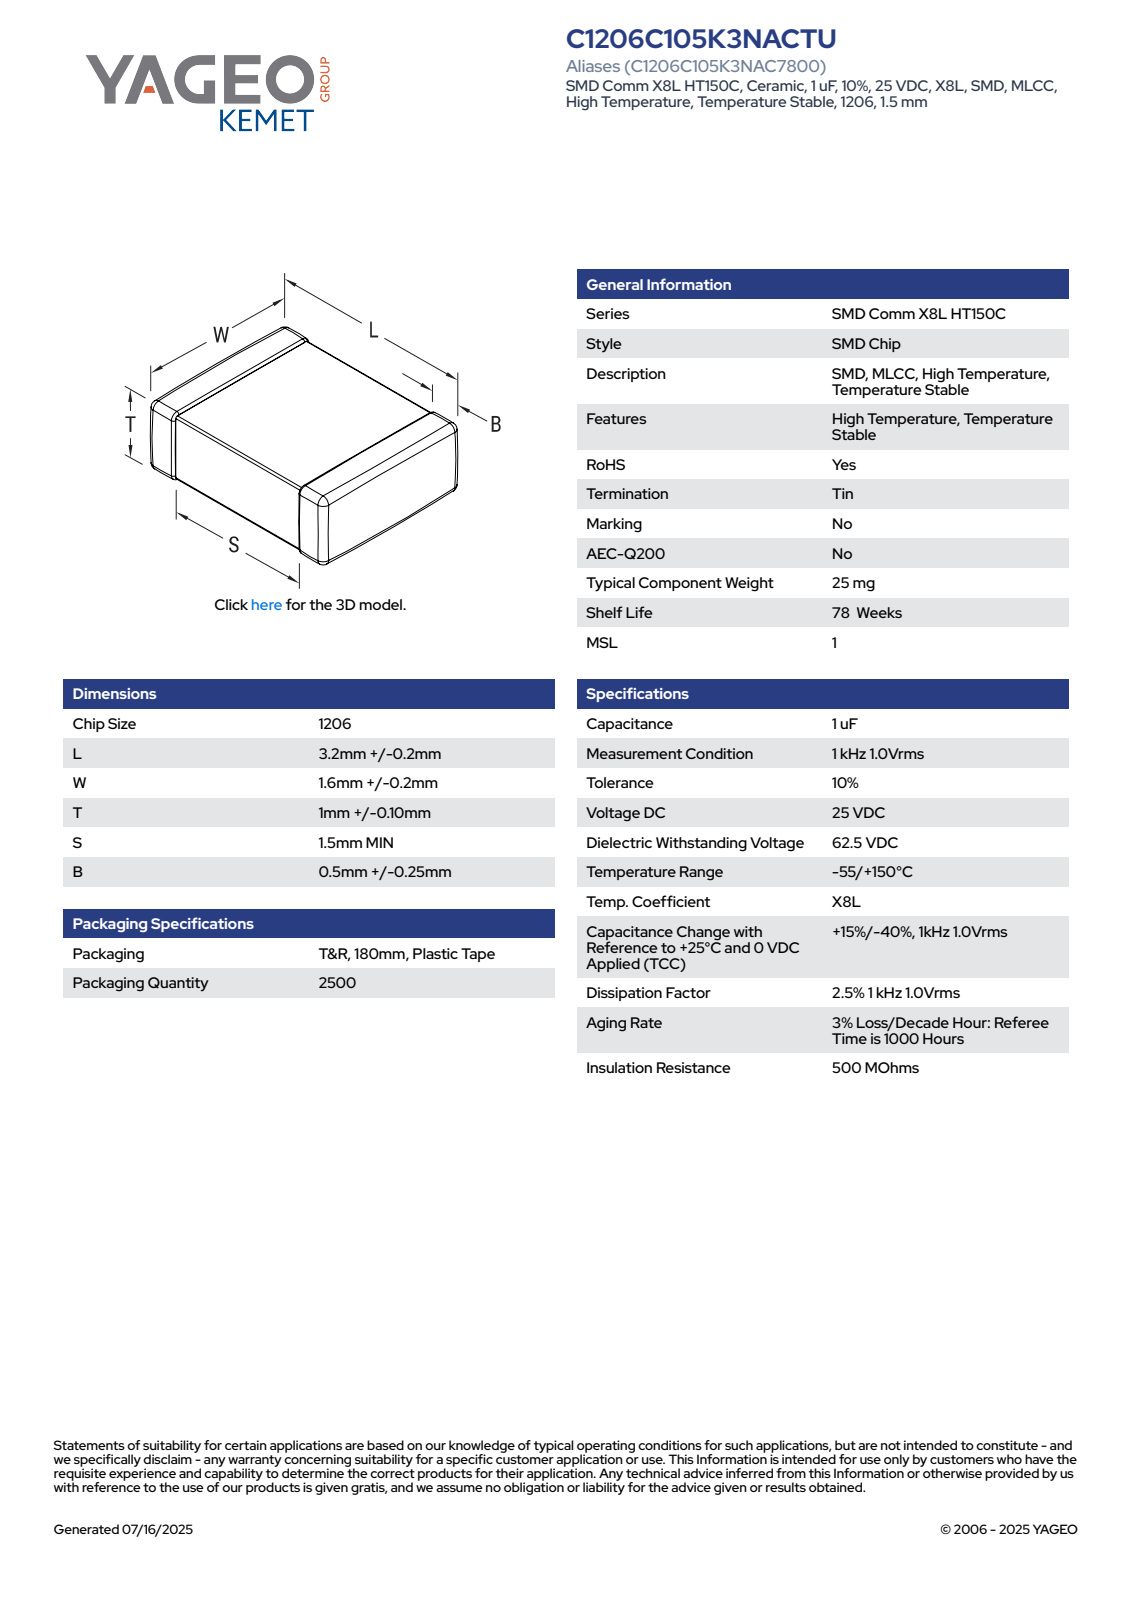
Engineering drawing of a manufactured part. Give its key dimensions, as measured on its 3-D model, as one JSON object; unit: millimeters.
{"part_name": "CCS_CCSTD_1206_L3.4W1.8S1.6T1.1B0.5", "step_written_by": "SolidWorks 2021 (AUTOMOTIVE_DESIGN)", "units": "millimeters", "bodies": {"solids": 4, "faces": 125, "planar": 71, "cylindrical": 38, "other": 16}, "overall_size": [3.4, 1.8, 1.1], "volume_mm3": 6, "surface_area_mm2": 23, "face_to_face_distances": [1.06, 1.02, 1.76, 1.1, 1.72, 3.4, 1.8, 1.07, 1.03, 1.57]}
